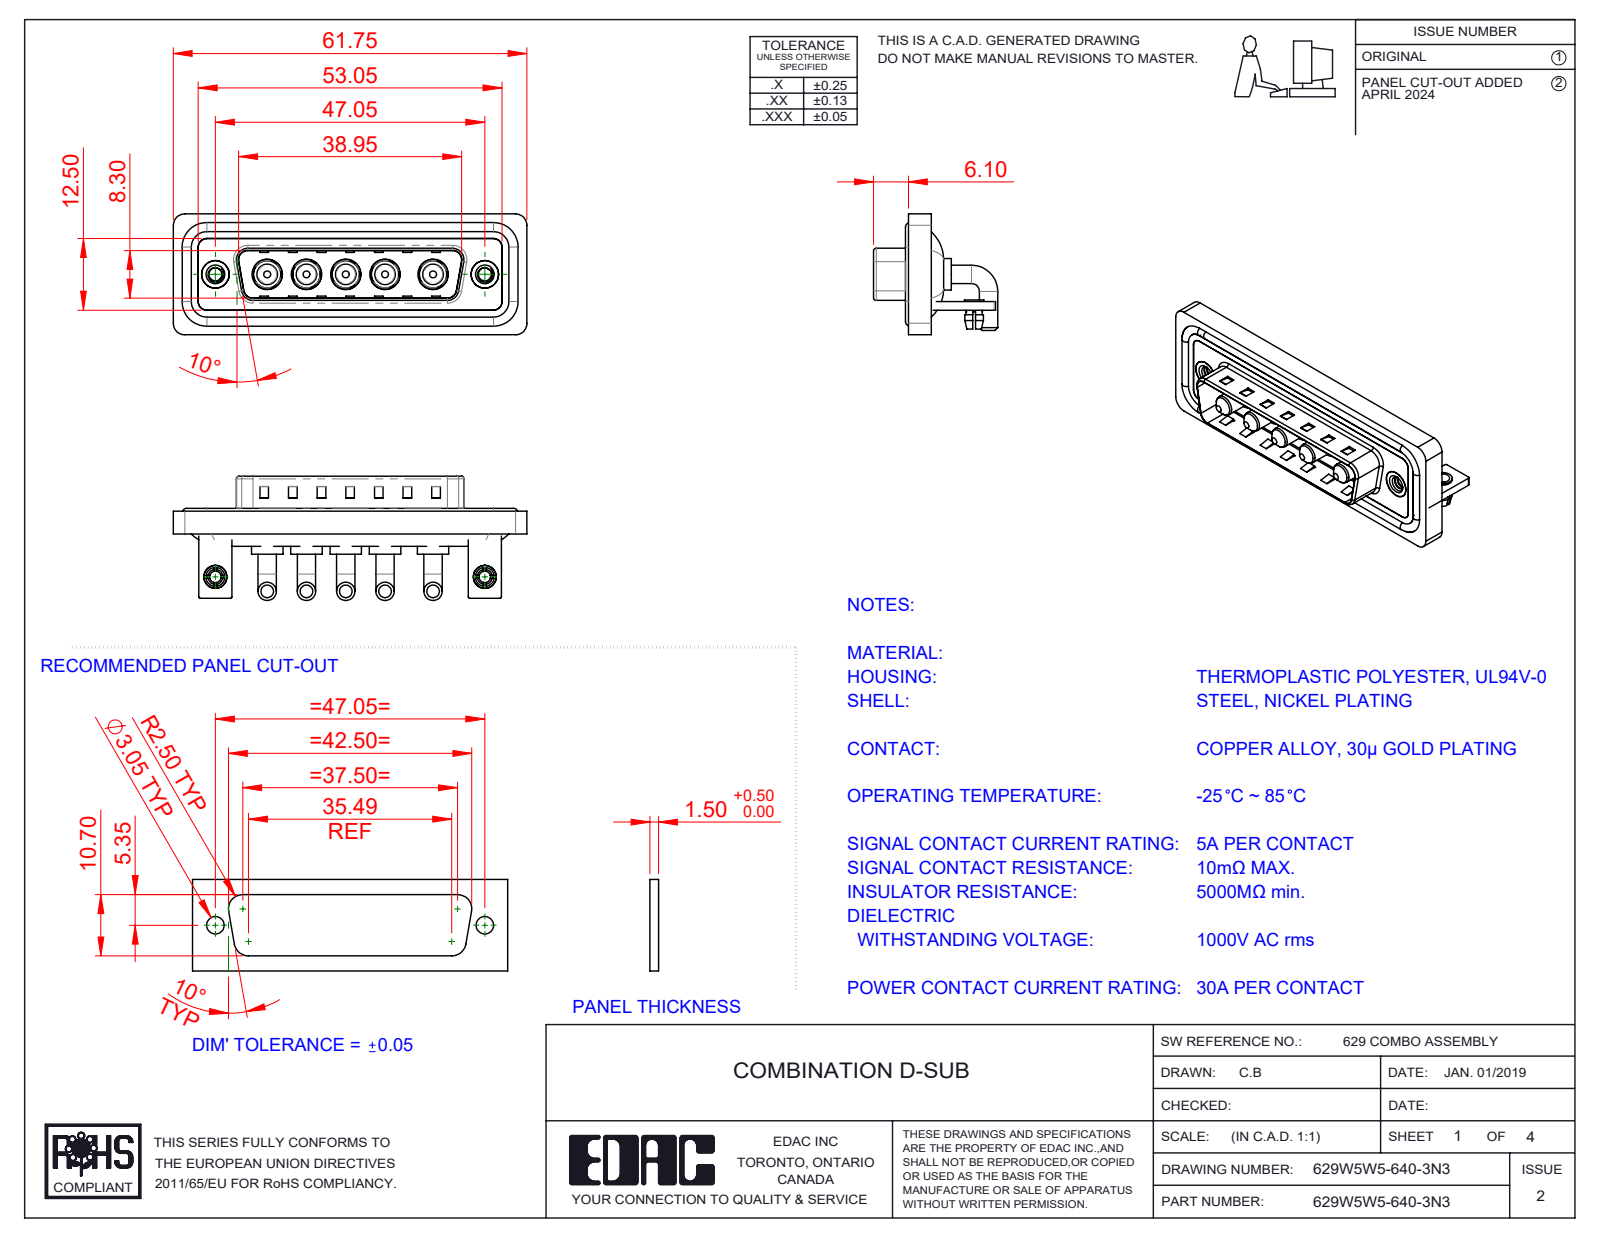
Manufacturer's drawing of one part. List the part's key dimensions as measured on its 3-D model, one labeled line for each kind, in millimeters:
Part name (STEP PRODUCT): 629Combo Shell Front_25 Contacts; 629Combo Stabilizer Bracket; 629W5W5-640-3N3; 629Combo Board Lock (+5 more)
STEP written by: SolidWorks 2023 (CONFIG_CONTROL_DESIGN)
Units: millimetres
Bodies: 21 solids, 830 faces (327 planar, 343 cylindrical, 160 other)
Overall size (bounding box): 61.75 × 21.7 × 21.1
Volume: 8 256 mm³ · Surface area: 13 161 mm²
Round holes (diameter × count): ⌀4.85 ×5, ⌀5.3 ×5, ⌀2 ×2, ⌀2.26 ×2, ⌀2.5 ×2, ⌀3.2 ×2, ⌀4 ×2, ⌀4.8 ×2, ⌀5 ×2
Round bosses / shafts (diameter × count): ⌀3.2 ×10, ⌀5.5 ×5, ⌀5.2 ×5, ⌀4.75 ×5, ⌀3.75 ×5, ⌀3.6 ×5, ⌀1.6 ×4, ⌀4.9 ×2
Partial cylindrical surfaces — rounded edges, fillets, slot ends (radius × count): R2 ×19, R1.5 ×18, R0.25 ×16, R0.5 ×9, R1.6 ×8, R2.1 ×5, R0.6 ×4, R0.65 ×4
Main face-to-face distances: 0.4, 1.5, 2.9, 0.8, 2.1, 1.1, 3.7, 4.5, 4.1, 1.2
Hole centre spacings: 6.86, 13.73, 47.05, 6.85, 6.87, 8.37, 8.38, 9.04
